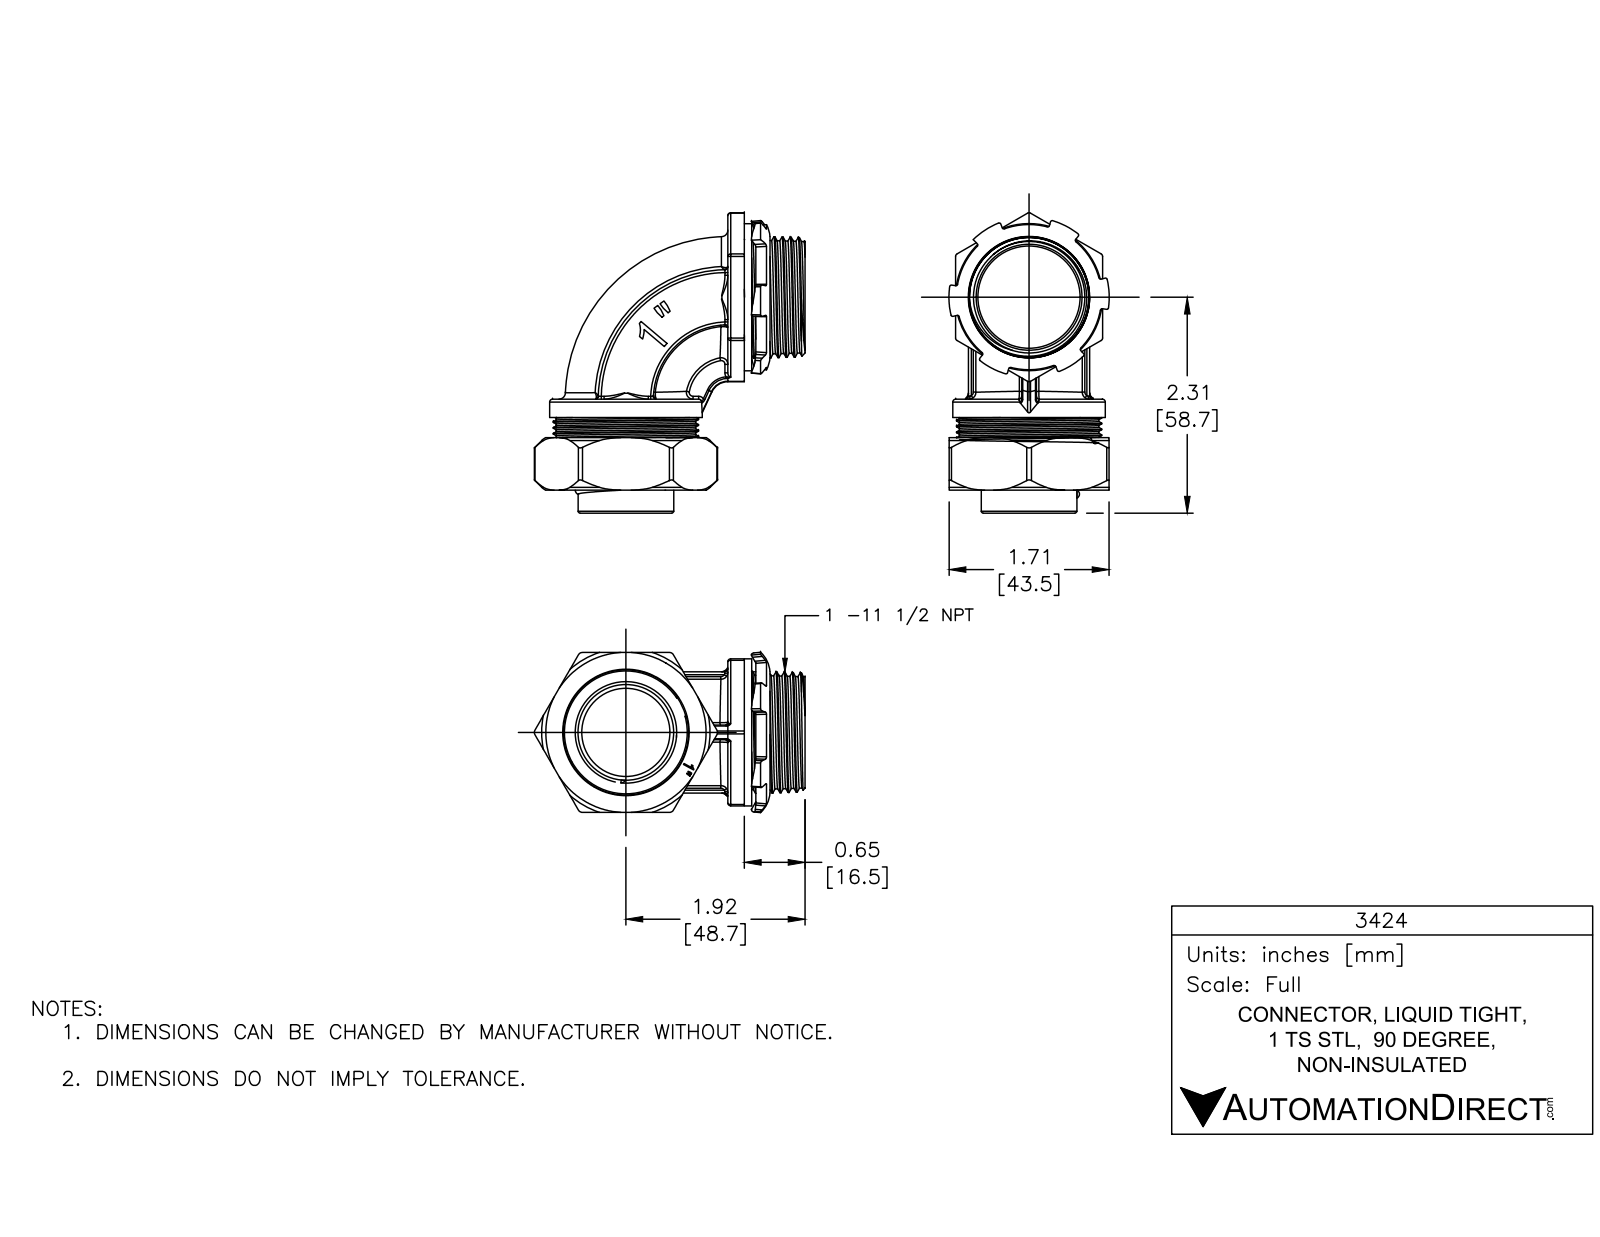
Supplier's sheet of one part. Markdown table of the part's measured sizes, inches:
| quantity | value |
| --- | --- |
| part name | 3424-5; 3424-2; 3424-3; 3424 (+3 more) |
| STEP written by | SolidWorks 2017 (AUTOMOTIVE_DESIGN) |
| units | inches |
| bodies | 6 solids, 611 faces (212 planar, 133 cylindrical, 266 other) |
| overall size | 3.217 × 2.9 × 1.717 |
| volume | 2.259 in³ |
| surface area | 59.57 in² |
| round holes (diameter × count) | 1.102 × 2, 0.15 × 1, 0.943 × 1, 0.985 × 1, 1.095 × 1, 1.215 × 1, 1.331 × 1, 1.335 × 1, 1.354 × 1, 1.386 × 1, 1.516 × 1 |
| round bosses / shafts (diameter × count) | 1.634 × 1, 1.575 × 1, 1.555 × 1, 1.496 × 1, 1.37 × 1, 1.024 × 1, 0.983 × 1, 0.122 × 1 |
| partial cylindrical surfaces (radius × count) | 0.031 × 21, 0.01 × 8, 0.05 × 6, 0.021 × 2, 0.046 × 2, 0.005 × 1, 0.013 × 1, 0.019 × 1 |
| main face-to-face distances | 1.713, 0.778, 0.207, 1.506, 1.299, 0.079, 0.177, 0.256, 0.975, 0.197 |
| hole center spacings | 0.775 |
